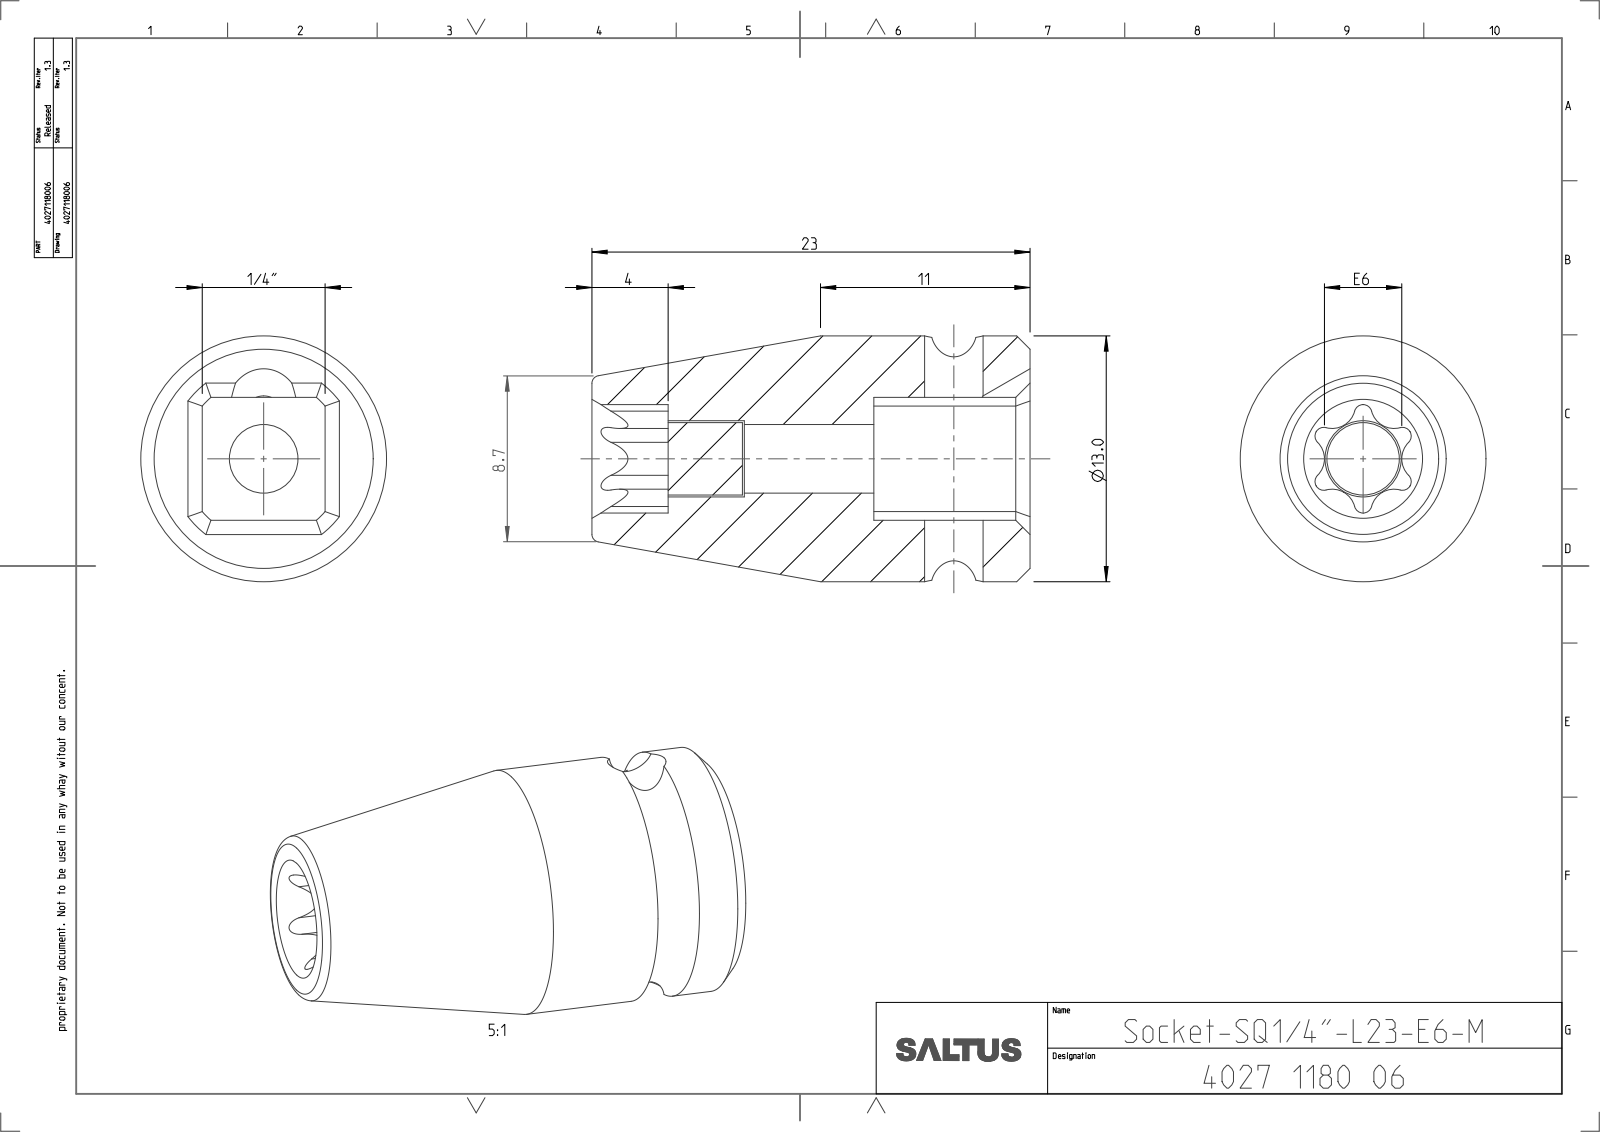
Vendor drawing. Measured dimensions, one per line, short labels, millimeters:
name: 4027118006
written by: CREO PARAMETRIC BY PTC INC, 2022414 (CONFIG_CONTROL_DESIGN)
unit: mm
bodies: 2 solids, 61 faces (16 planar, 31 cylindrical, 14 other)
size: 23 × 12.9 × 12.9
volume: 1 931 mm³; area: 1 501 mm²
holes: 1× ⌀3.07, 1× ⌀3.6, 1× ⌀4
bosses: 1× ⌀12.9, 1× ⌀3.8
rounds: 6× R0.46, 6× R1.22, 1× R2, 1× R4.25
face distances: 6.46, 8.2, 4, 23, 14.8, 19, 10.8, 15.1, 6.9, 3.9
